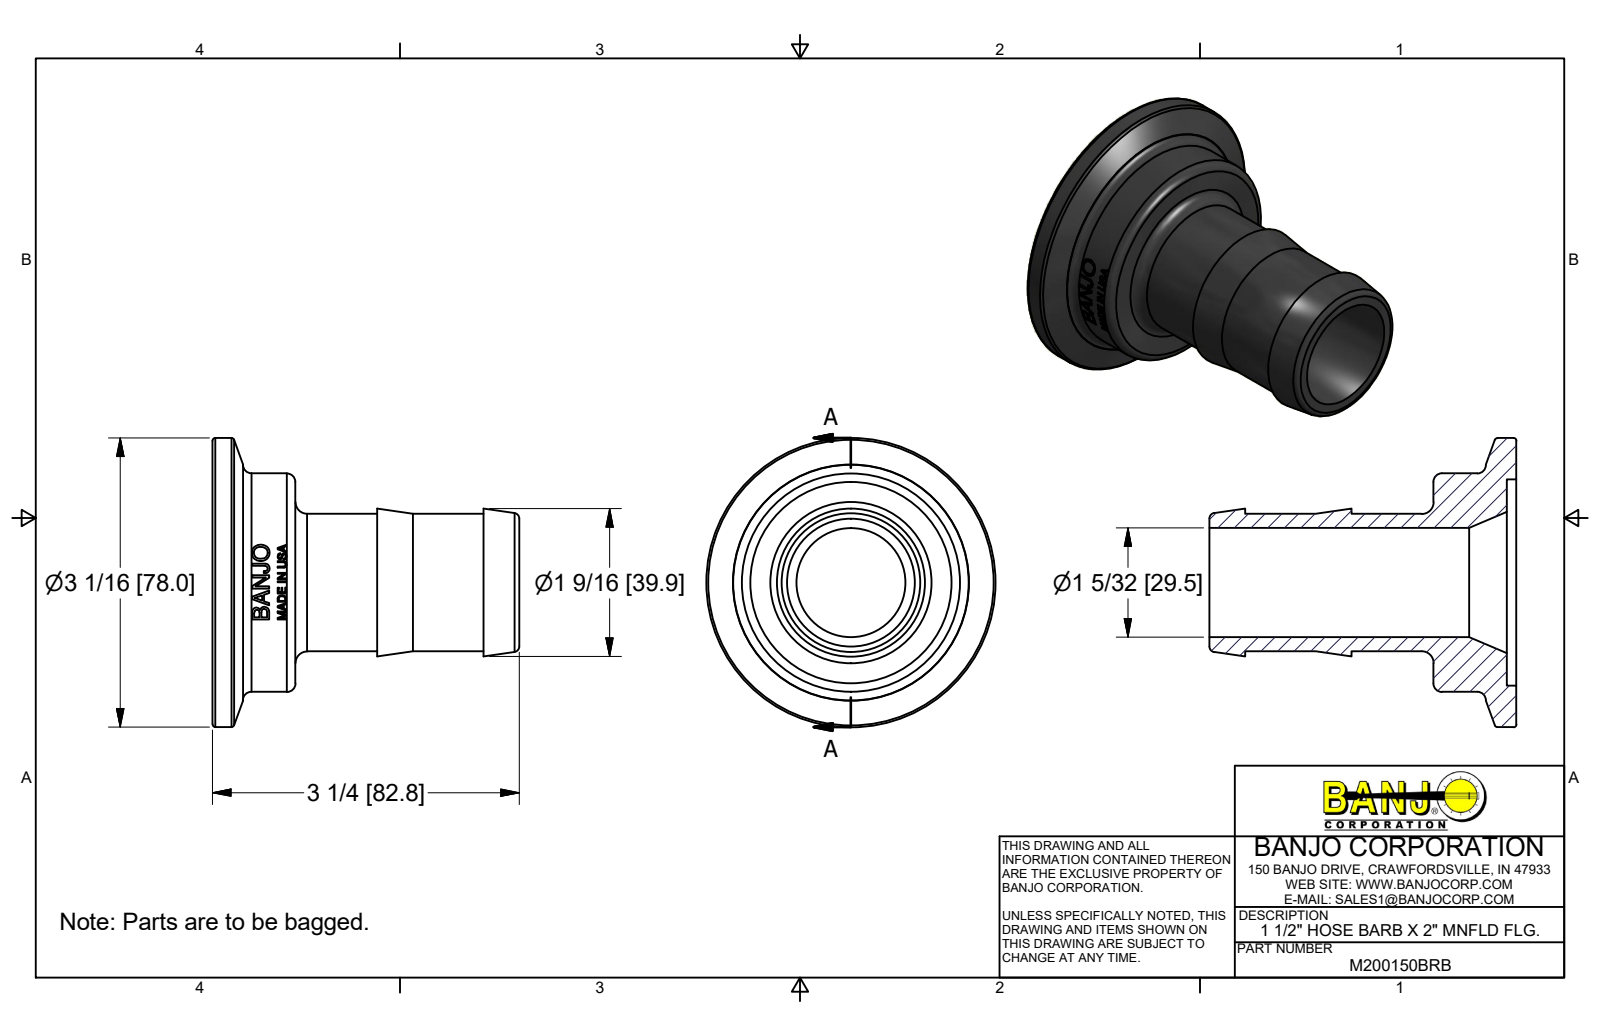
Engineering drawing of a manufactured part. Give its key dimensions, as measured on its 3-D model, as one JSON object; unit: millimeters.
{"part_name": "M200150BRB", "step_written_by": "Autodesk Inventor 2014 (AUTOMOTIVE_DESIGN)", "units": "millimeters", "bodies": {"solids": 1, "faces": 396, "planar": 187, "cylindrical": 45, "other": 164}, "overall_size": [82.8, 77.98, 77.98], "volume_mm3": 79571, "surface_area_mm2": 27103, "round_holes": [[29.46, 1], [55.63, 1]], "round_bosses_or_shafts": [[77.98, 1], [58.93, 1], [37.08, 1]], "partial_cylinders_radius": [[28.7, 1]], "face_to_face_distances": [2.54, 19.81, 22.35, 60.45, 80.26, 82.8, 9.65, 50.8, 70.61, 73.15]}
